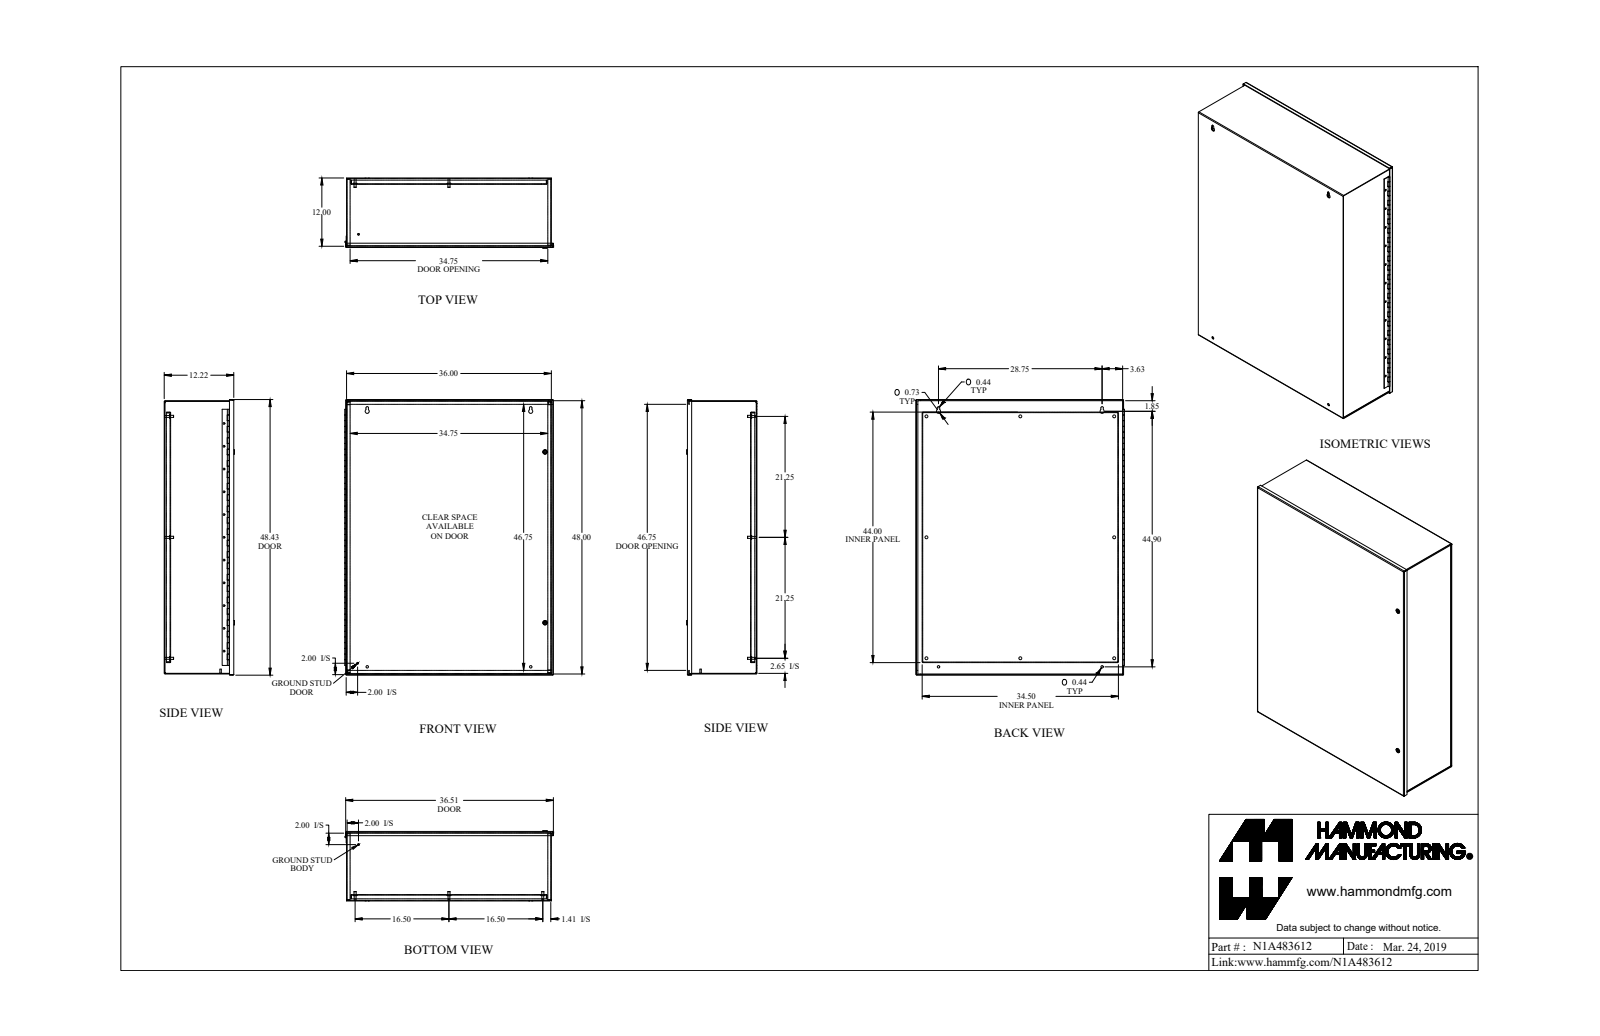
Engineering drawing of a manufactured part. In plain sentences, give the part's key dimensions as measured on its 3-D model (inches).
The part is named "N1A483612". Its 3-D file was written by "SolidWorks 2018 (AUTOMOTIVE_DESIGN)". It is 31 solids with 997 faces: 521 planar, 408 cylindrical and 68 other. Overall it measures 48.43 by 36.668 by 12.342 inches. Its volume is 708.5 cubic inches and its surface area 15 075 square inches. Round holes: 11 of diameter 0.304, 8 of diameter 0.5, 4 of diameter 0.307, 4 of diameter 0.445, 3 of diameter 0.734, 2 of diameter 0.437, 2 of diameter 0.516, 1 of diameter 0.188. Round bosses or shafts: 8 of diameter 0.65, 8 of diameter 0.375, 8 of diameter 0.33, 4 of diameter 1, 2 of diameter 0.788, 2 of diameter 0.535, 2 of diameter 0.496, 2 of diameter 0.281. Partial cylindrical surfaces (rounded edges, fillets, slot ends): 16 of radius 0.048, 16 of radius 0.143, 6 of radius 0.125, 5 of radius 0.03, 3 of radius 0.219, 2 of radius 0.06, 2 of radius 0.153, 2 of radius 0.315. The main face-to-face distances are 0.095, 1.032, 0.095, 12.03, 12.125, 12.125, 12.22, 11.093, 1.127, 10.998. The hole center spacings are 4, 8, 12, 16, 20, 24, 28, 22.251.
